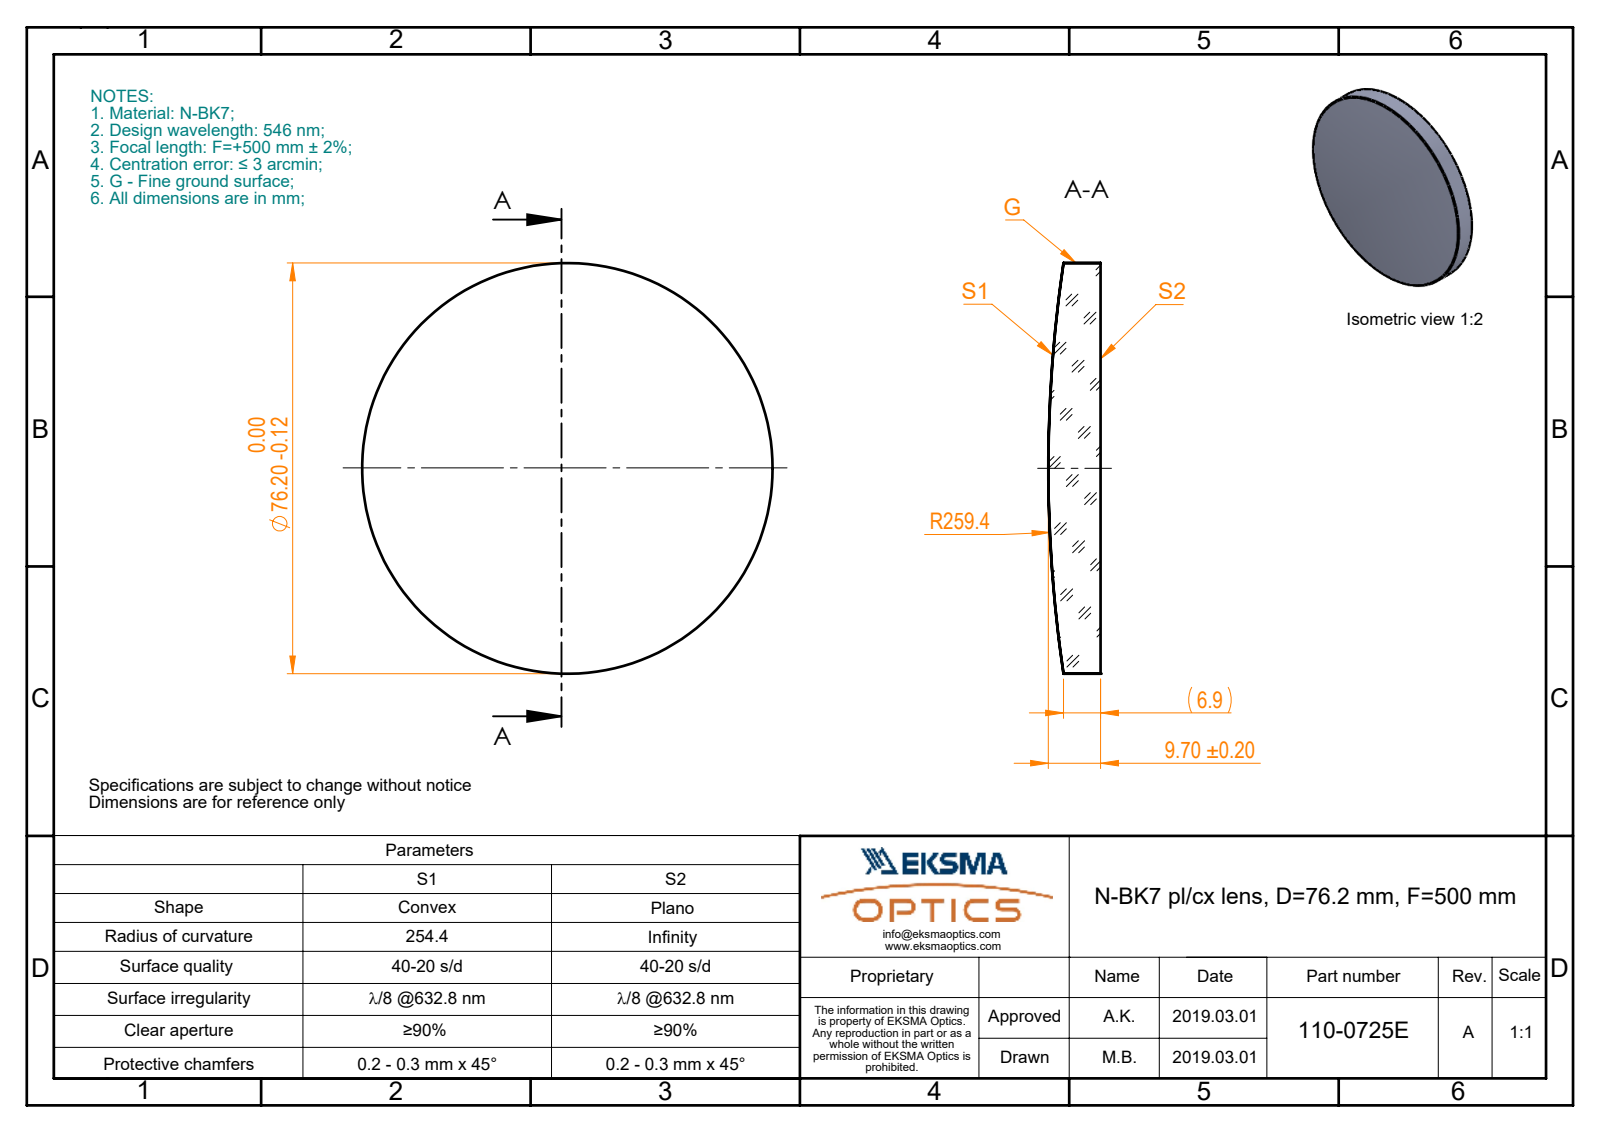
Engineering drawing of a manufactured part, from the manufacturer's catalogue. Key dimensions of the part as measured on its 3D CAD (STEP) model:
Part name (STEP PRODUCT): 110-0725E BK7 pl-cx 76.2 F500
STEP written by: SolidWorks 2017 (CONFIG_CONTROL_DESIGN)
Units: millimetres
Bodies: 1 solid, 5 faces (1 planar, 2 cylindrical, 2 other)
Overall size (bounding box): 76.2 × 76.2 × 9.7
Volume: 37 832 mm³ · Surface area: 10 794 mm²
Round bosses / shafts (diameter × count): ⌀76.2 ×1
